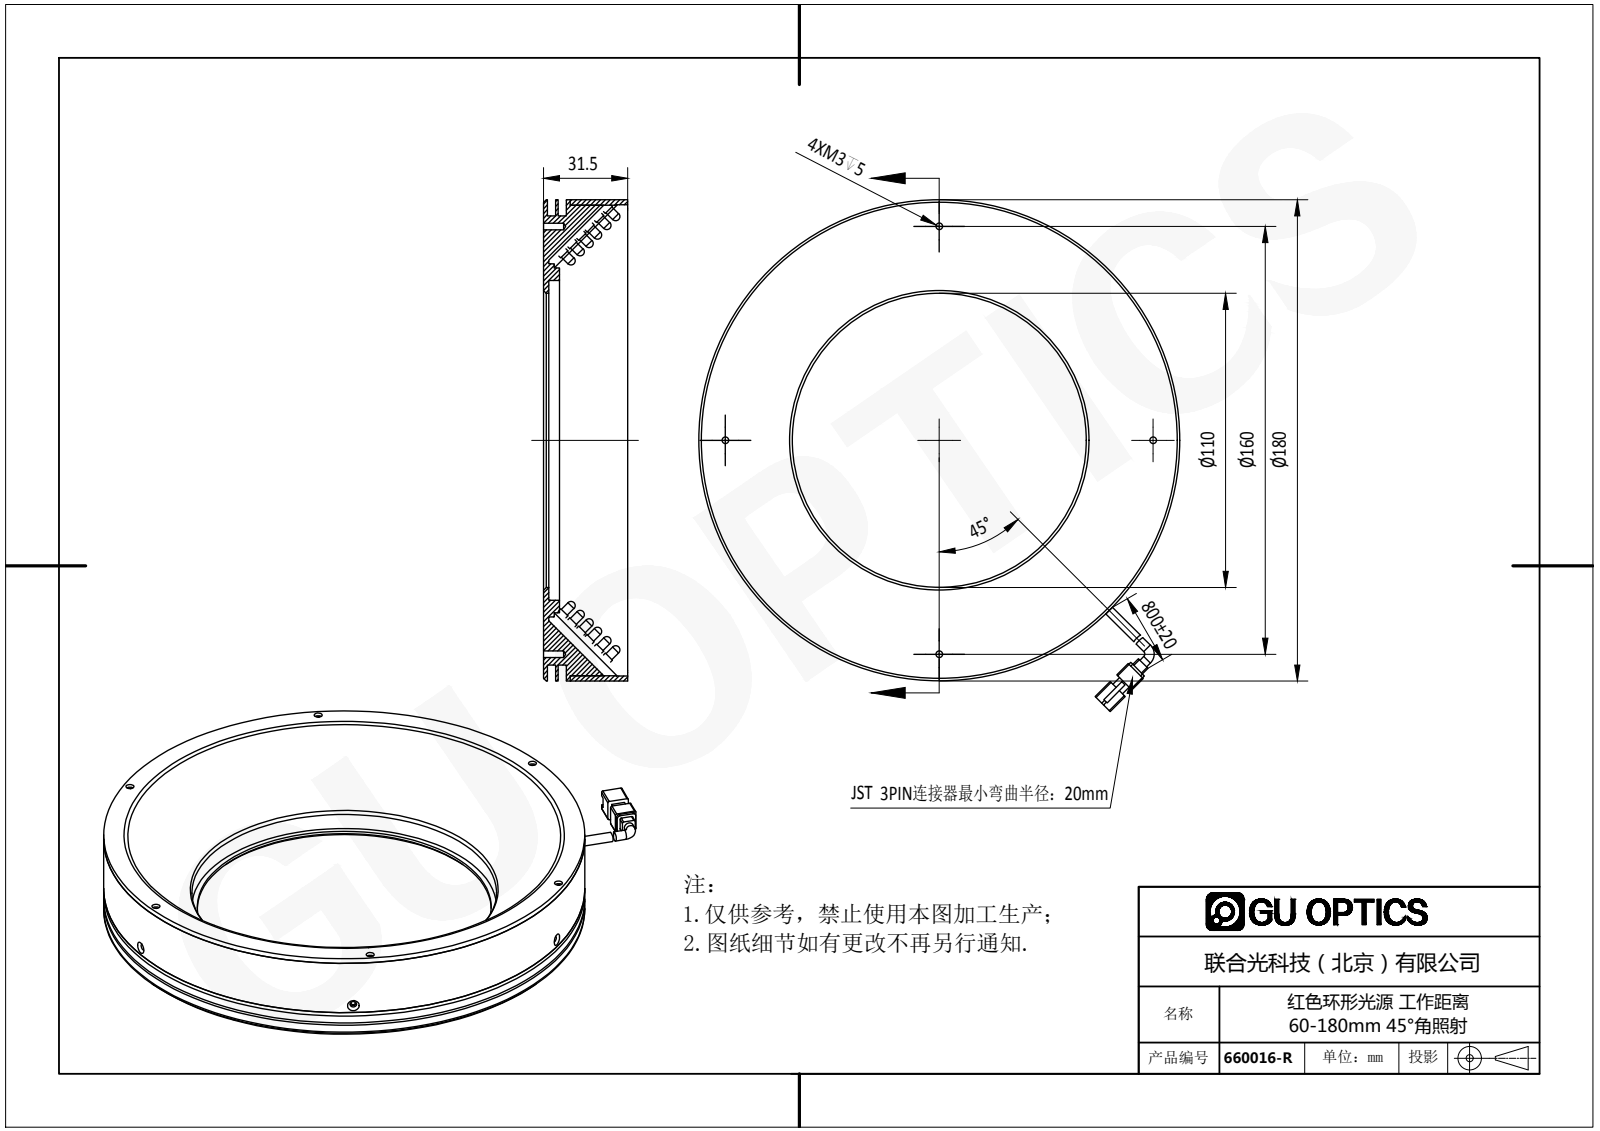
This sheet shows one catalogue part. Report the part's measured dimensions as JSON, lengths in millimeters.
{"part_name": "660016-R", "step_written_by": "SolidWorks 2016 (AUTOMOTIVE_DESIGN)", "units": "millimeters", "bodies": {"solids": 546, "faces": 9482, "planar": 6561, "cylindrical": 2312, "other": 609}, "overall_size": [191.47, 180, 33.5], "volume_mm3": 236719, "surface_area_mm2": 217058, "round_holes": [[3.5, 7], [1.25, 6], [1.5, 6], [3, 6], [1.6, 4], [2.5, 4], [2.4, 3], [110, 1], [114, 1], [119.6, 1], [172.4, 1]], "round_bosses_or_shafts": [[3.8, 540], [3, 540], [3.5, 2], [180, 1], [176, 1], [168, 1], [132, 1], [129, 1]], "partial_cylinders_radius": [[0.5, 8], [1, 4], [7.5, 1]], "face_to_face_distances": [4, 31.5, 2, 0.5, 1.5, 4.5, 3, 2.5, 5.5, 8.5], "hole_center_spacings": [87.5, 151.56, 39.06, 51.47, 128.2, 151.55, 167.26, 170.58]}
